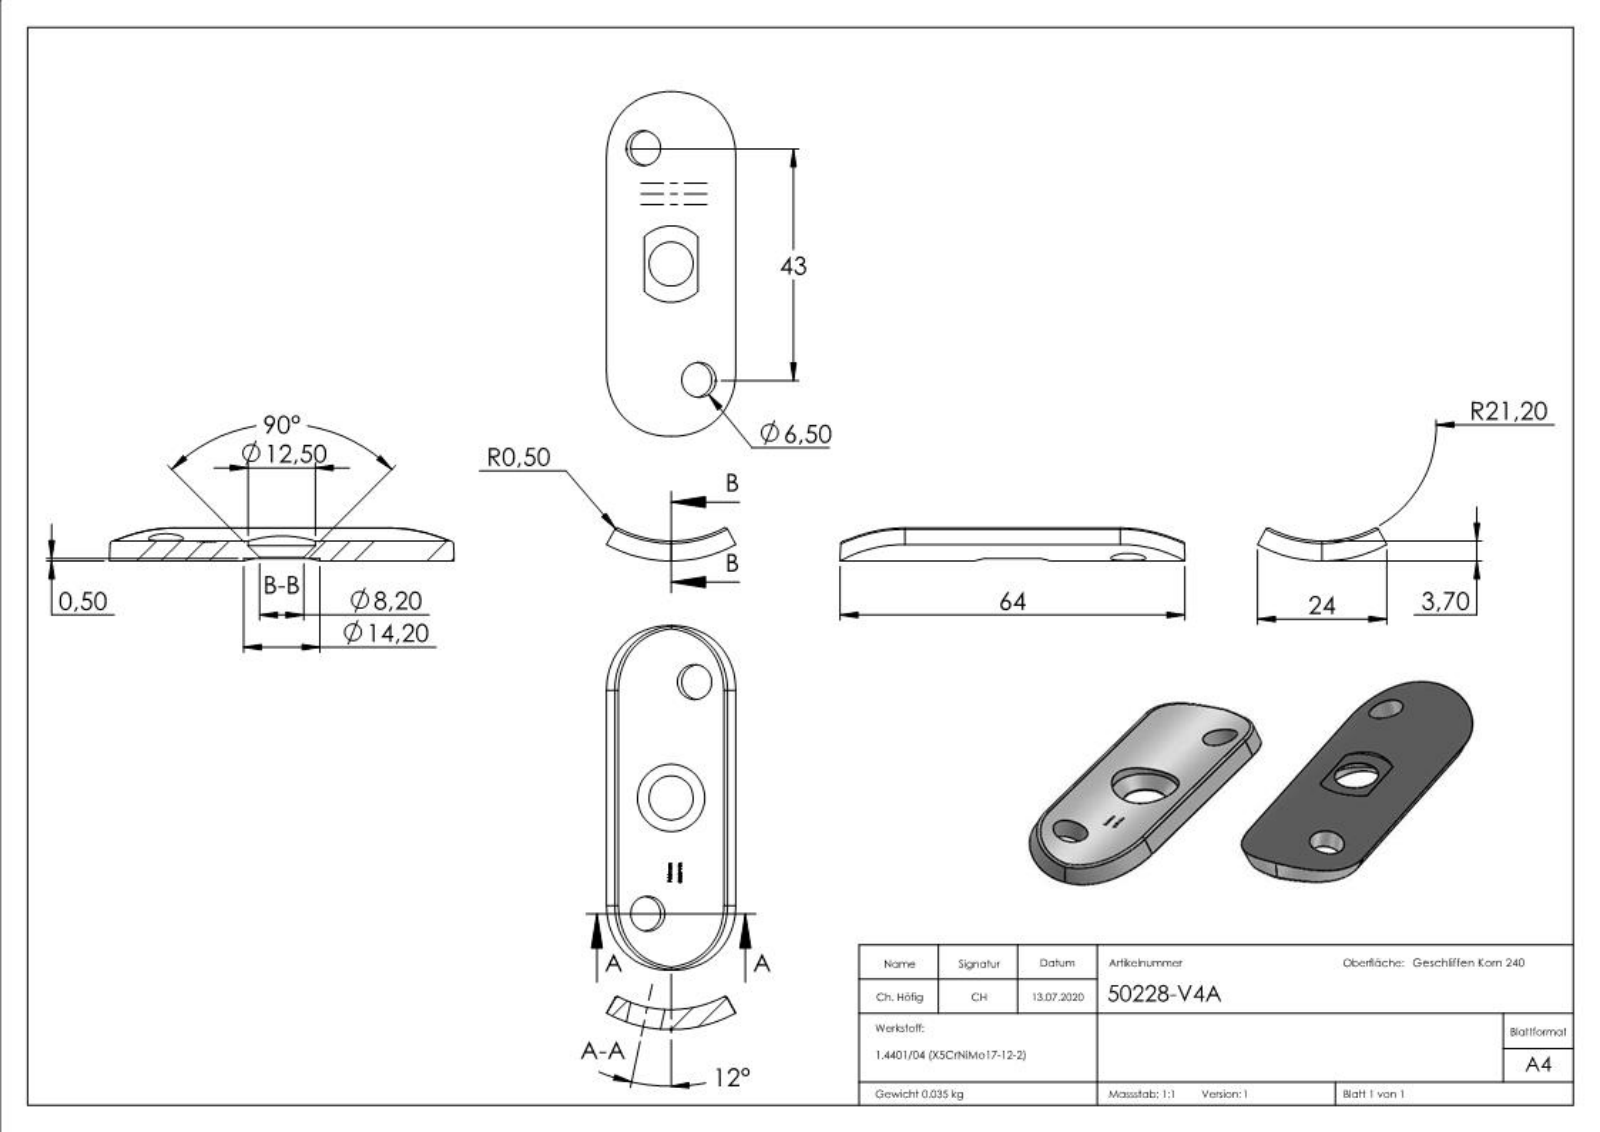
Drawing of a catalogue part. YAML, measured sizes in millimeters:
part_name: "50228-V4A"
step_written_by: "SolidWorks 2018 (CONFIG_CONTROL_DESIGN)"
units: millimeters
bodies: {solids: 1, faces: 254, planar: 110, cylindrical: 44, other: 100}
overall_size: [64, 24, 6.15]
volume: 4398
surface_area: 3266
round_holes:
  - {diameter: 6.5, count: 1}
  - {diameter: 6.5, count: 1}
  - {diameter: 8.2, count: 1}
  - {diameter: 12.5, count: 1}
partial_cylinders:
  - {radius: 12, count: 4}
  - {radius: 0.5, count: 2}
  - {radius: 7.1, count: 1}
  - {radius: 21.2, count: 1}
  - {radius: 21.3, count: 1}
  - {radius: 24.9, count: 1}
face_to_face_distances: [0.53, 0.31, 1.9, 0.55, 0.45, 1.6, 0.5, 1.84, 1.68, 2.08]
